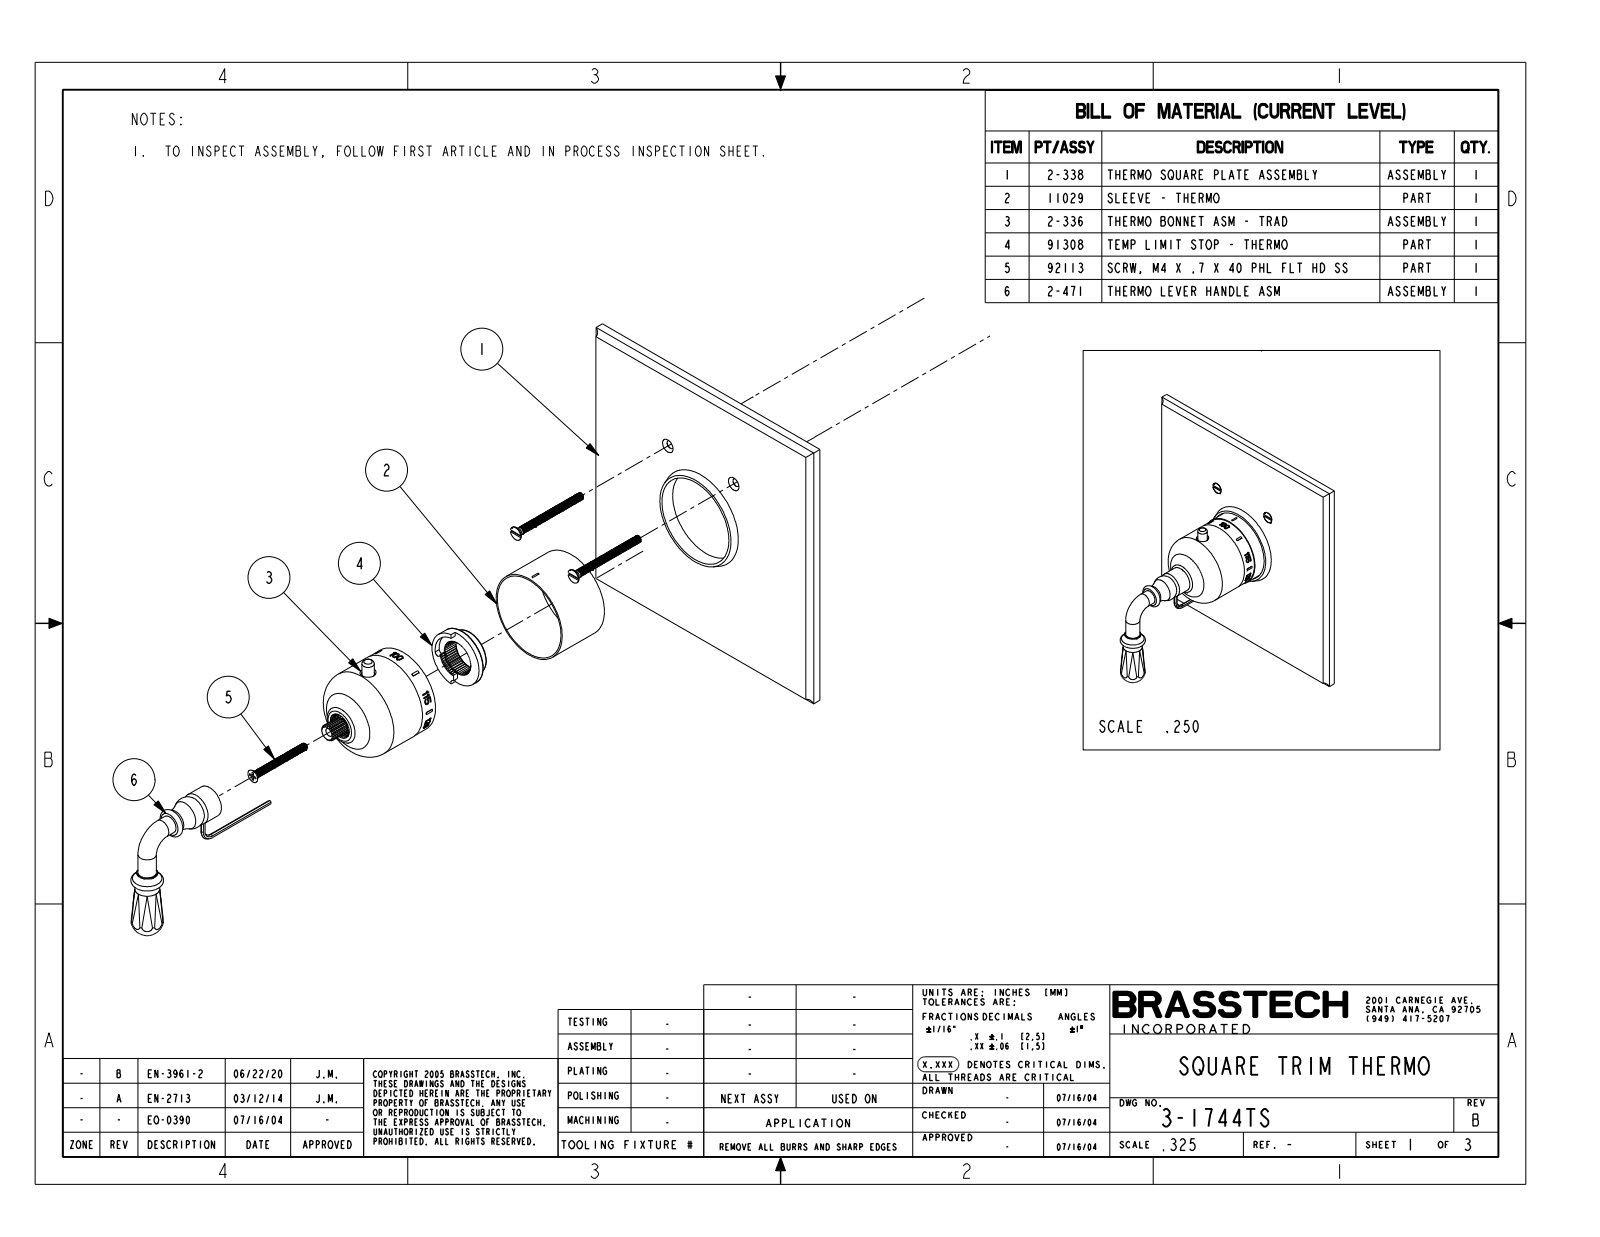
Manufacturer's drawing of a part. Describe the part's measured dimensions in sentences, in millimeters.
The part is named "3-1744TS". Its 3-D file was written by "CREO PARAMETRIC BY PTC INC, 2018400 (CONFIG_CONTROL_DESIGN)". It is 1 solid with 422 faces: 341 planar, 43 cylindrical and 38 other. Overall it measures 165.1 by 165.1 by 124.8 millimeters. Its volume is 332 300 cubic millimeters and its surface area 71 680 square millimeters. Round bosses or shafts: 2 of diameter 9.9, 1 of diameter 50, 1 of diameter 49.3, 1 of diameter 49, 1 of diameter 17.9, 1 of diameter 13.3, 1 of diameter 12.1, 1 of diameter 6.6. Partial cylindrical surfaces (rounded edges, fillets, slot ends): 4 of radius 3.2, 1 of radius 24.6. The main face-to-face distances are 8, 165.1, 20.6, 12.7, 99.2, 91.3, 78.6, 30.6, 52.6, 112.5.
